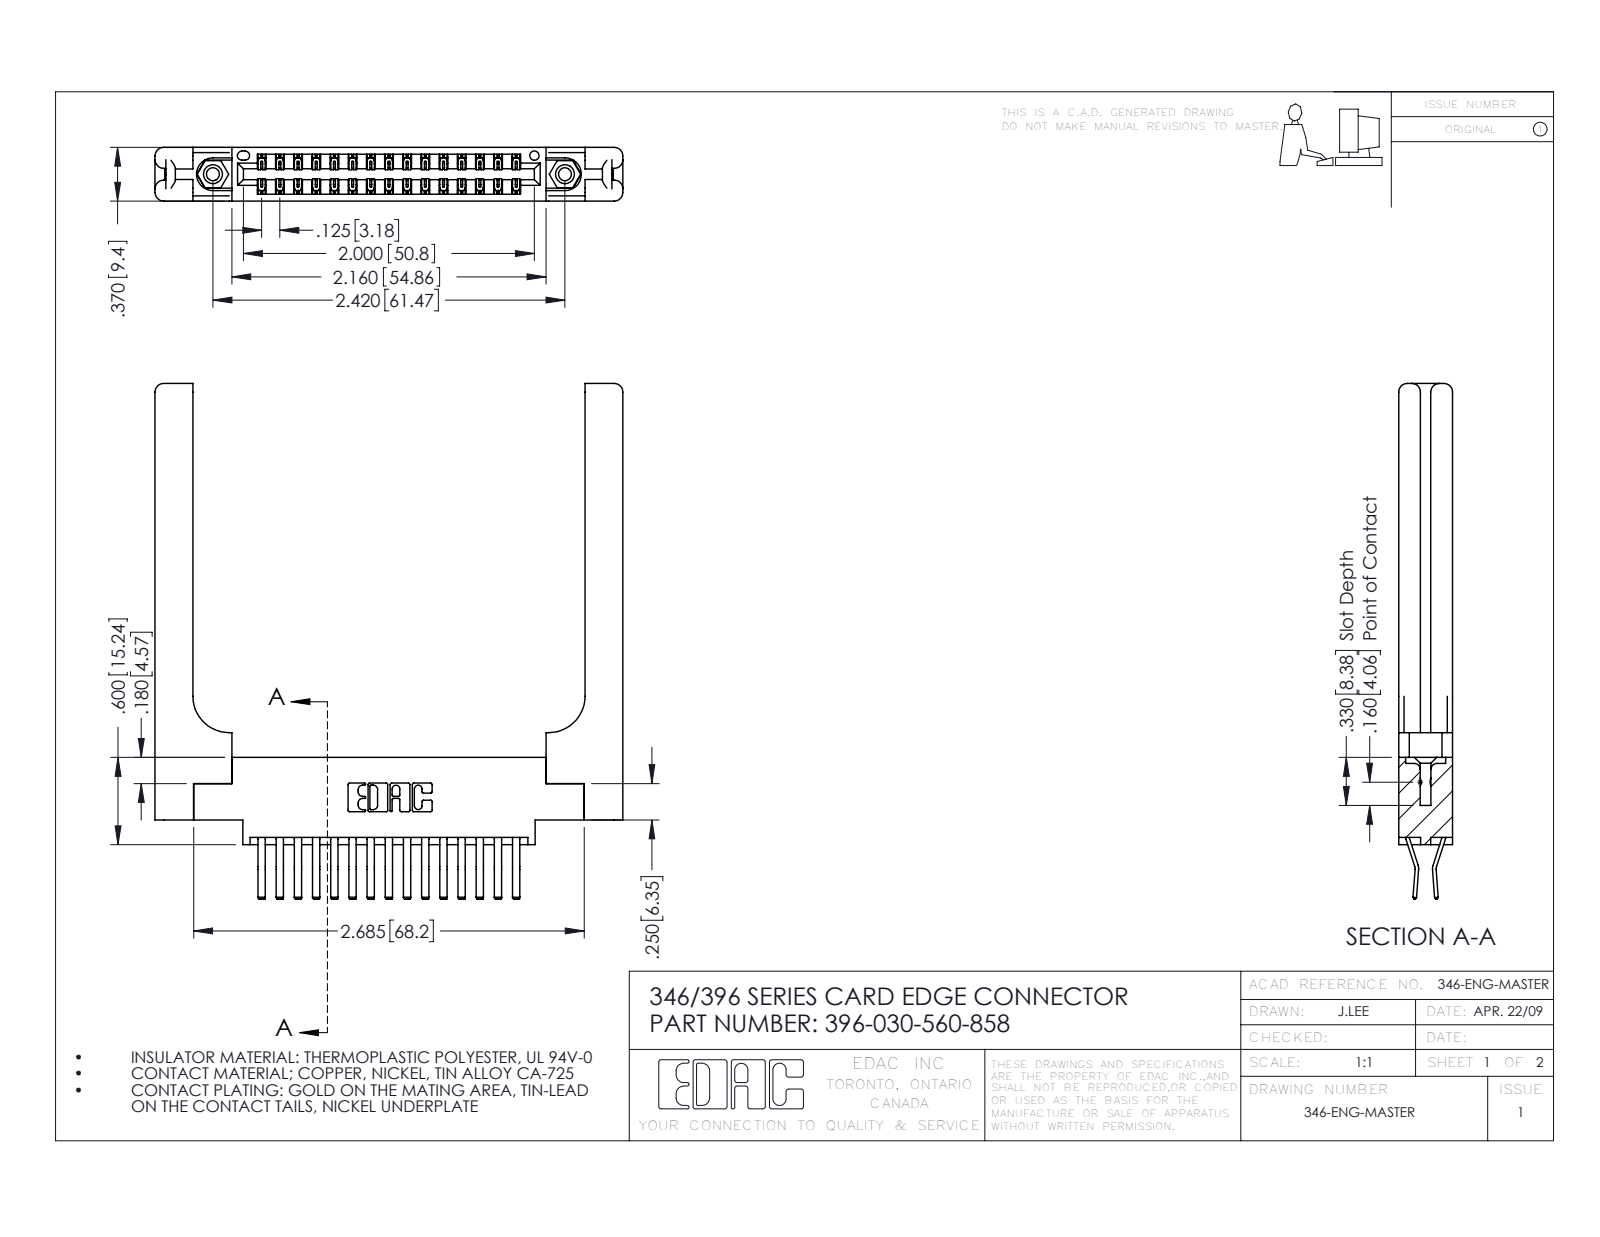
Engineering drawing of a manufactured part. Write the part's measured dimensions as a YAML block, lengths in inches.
part_name: "346 Part_0.170 Offset - 0.156 Dia-TH; 396-030-560-858; 345-292-001_560 Tail; 346-220-058_345-220-058 (+1 more)"
step_written_by: "SolidWorks 2016 (CONFIG_CONTROL_DESIGN)"
units: inches
bodies: {solids: 35, faces: 2002, planar: 1278, cylindrical: 664, other: 60}
overall_size: [3.545, 3.216, 0.37]
volume: 0.933
surface_area: 24.76
round_holes:
  - {diameter: 0.089, count: 2}
  - {diameter: 0.125, count: 2}
  - {diameter: 0.156, count: 2}
  - {diameter: 0.064, count: 1}
round_bosses_or_shafts:
  - {diameter: 0.155, count: 2}
partial_cylinders:
  - {radius: 0.006, count: 45}
  - {radius: 0.01, count: 22}
  - {radius: 0.06, count: 16}
  - {radius: 0.007, count: 6}
  - {radius: 0.031, count: 6}
  - {radius: 0.026, count: 3}
  - {radius: 0.01, count: 2}
  - {radius: 0.014, count: 2}
face_to_face_distances: [0.37, 0.15, 0.072, 0.148, 0.048, 0.322, 0.025, 0.25, 0.102, 0.22]
hole_center_spacings: [0.246, 2.213, 2.42]
